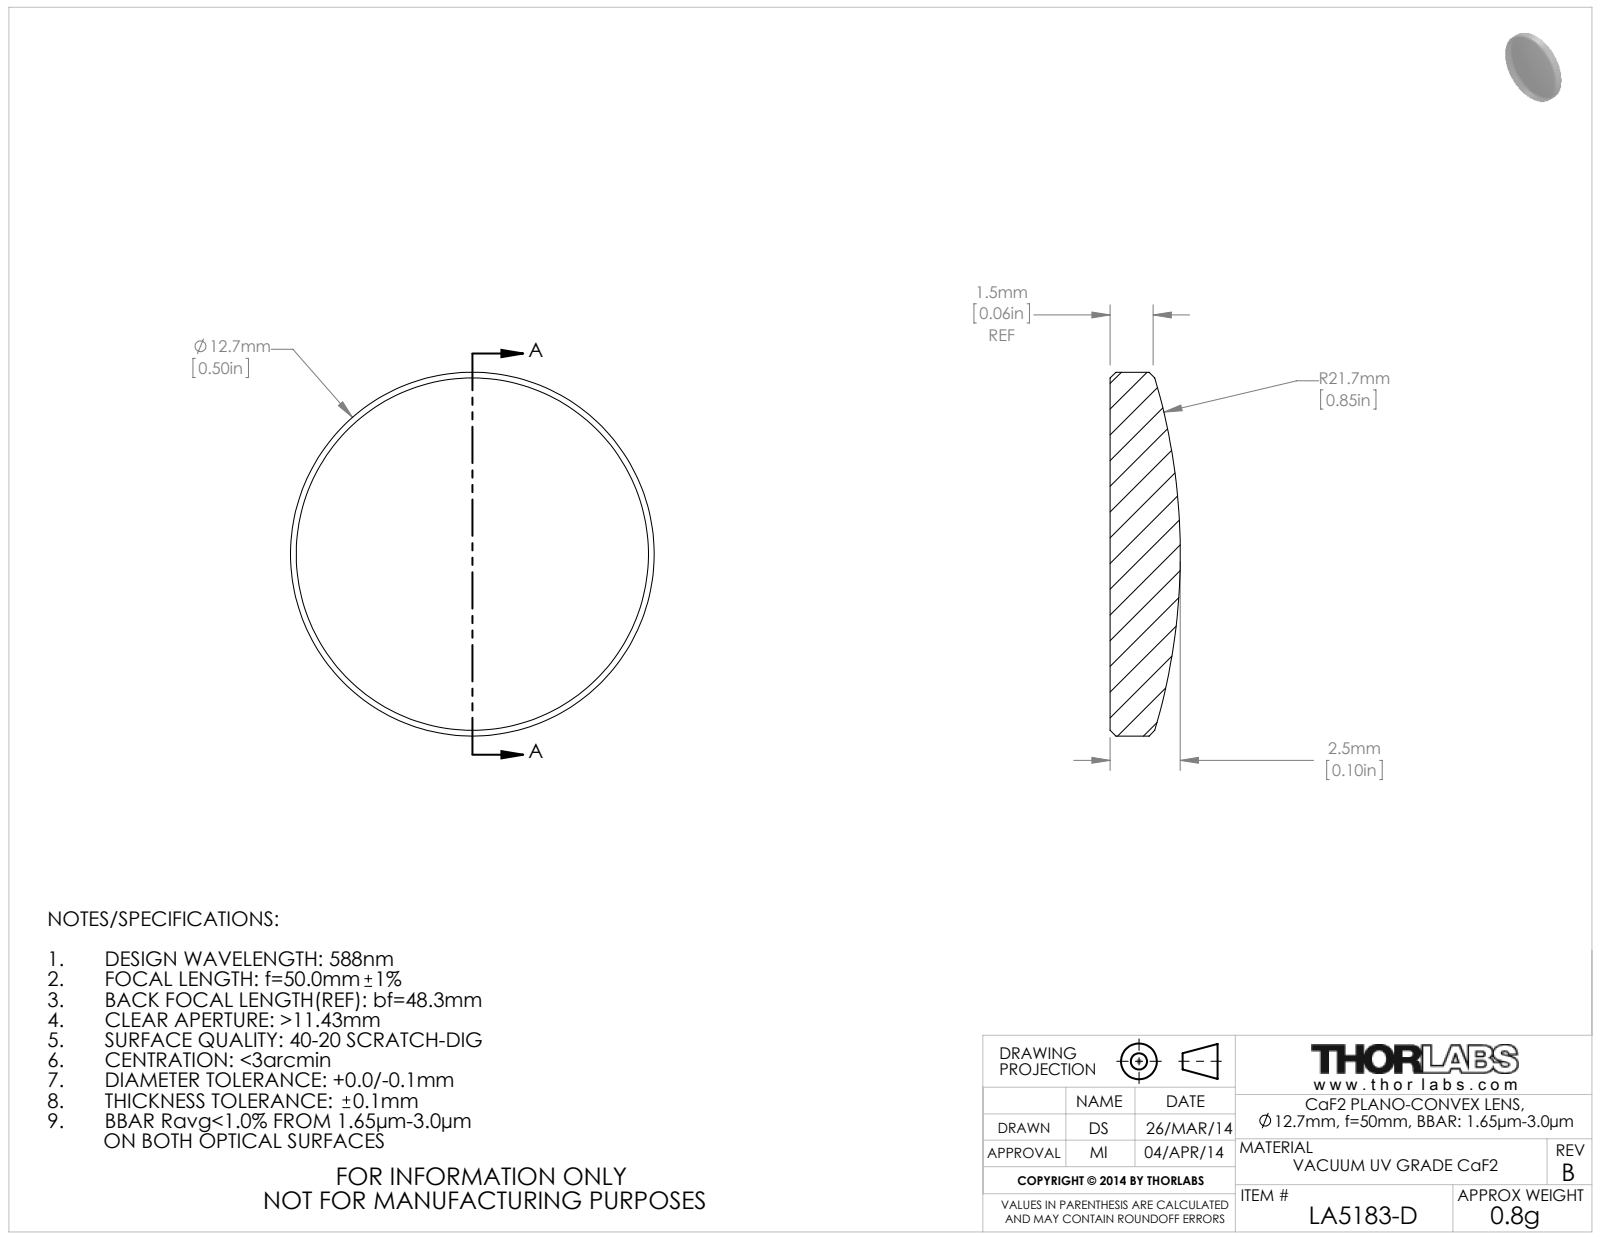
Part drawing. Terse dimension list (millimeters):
name: 22970-E0W
written by: SolidWorks 2011 (AUTOMOTIVE_DESIGN)
unit: mm
bodies: 0 solids, 5 faces (1 planar, 2 cylindrical, 2 other)
size: 12.7 × 12.7 × 2.45
bosses: 1× ⌀12.7
